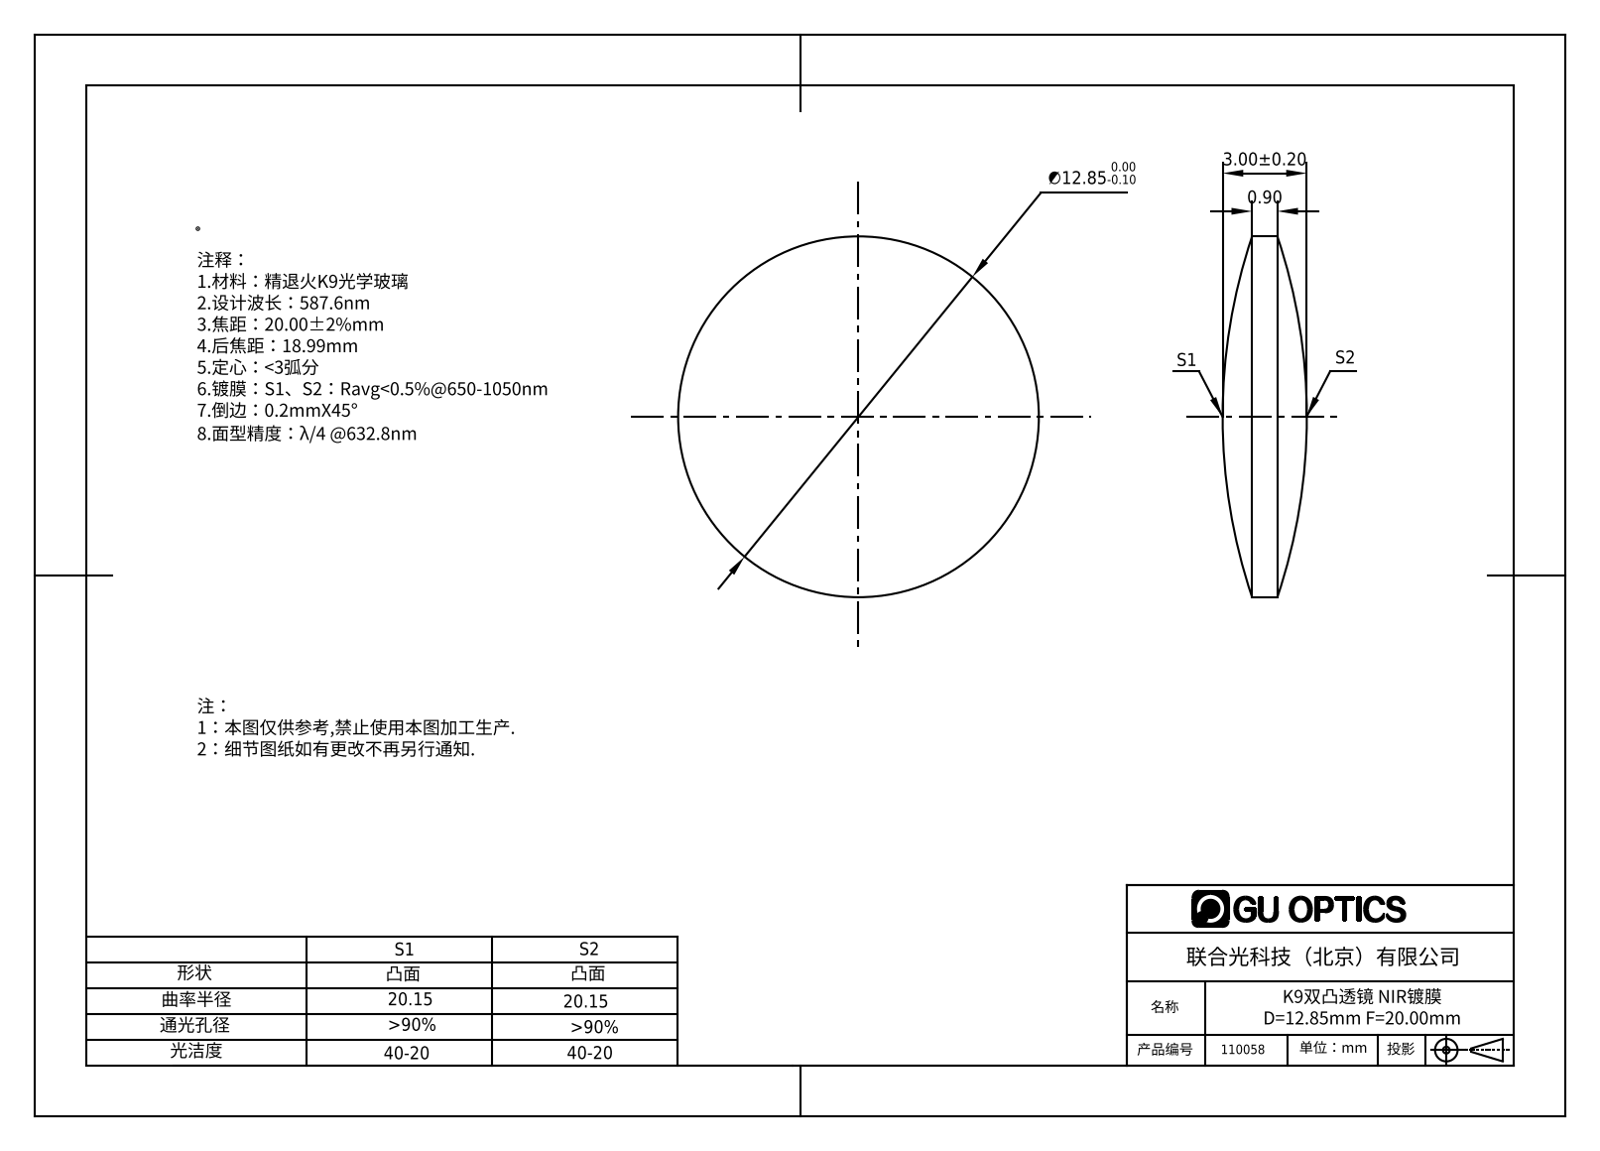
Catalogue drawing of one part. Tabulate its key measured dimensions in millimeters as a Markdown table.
| quantity | value |
| --- | --- |
| part name | 110014 |
| STEP written by | SolidWorks 2016 (CONFIG_CONTROL_DESIGN) |
| units | millimeters |
| bodies | 1 solid, 6 faces (0 planar, 2 cylindrical, 4 other) |
| overall size | 12.85 × 12.85 × 3 |
| volume | 254 mm³ |
| surface area | 303 mm² |
| round bosses / shafts (diameter × count) | 12.85 × 1 |
